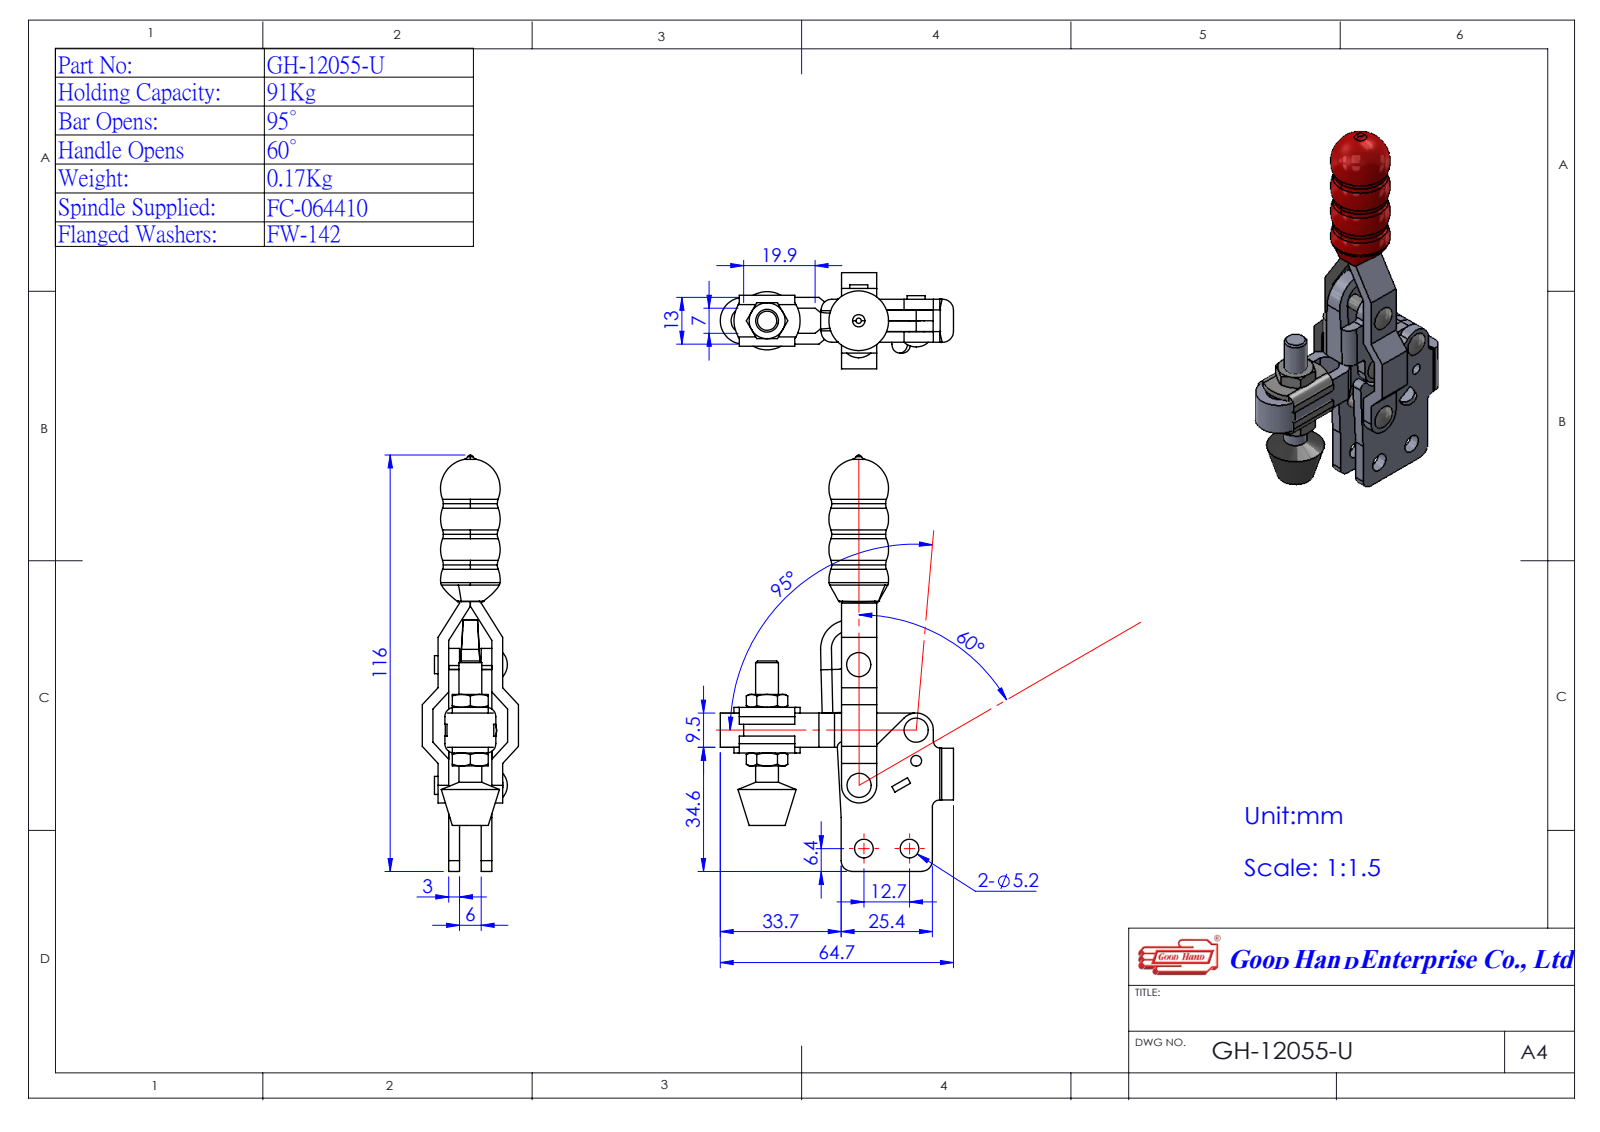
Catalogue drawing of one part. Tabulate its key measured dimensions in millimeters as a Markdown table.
| quantity | value |
| --- | --- |
| part name | Group1^GH-12055-U(簡化)-1; Group5^GH-12055-U(簡化)-1; Group3^GH-12055-U(簡化)-1; Group4^GH-12055-U(簡化)-1 (+2 more) |
| STEP written by | SolidWorks 2016 (AUTOMOTIVE_DESIGN) |
| units | millimeters |
| bodies | 6 solids, 331 faces (138 planar, 117 cylindrical, 76 other) |
| overall size | 115.85 × 64.65 × 26.8 |
| volume | 26 939 mm³ |
| surface area | 18 821 mm² |
| round holes (diameter × count) | 3 × 5, 5.2 × 2 |
| round bosses / shafts (diameter × count) | 5 × 4, 4.05 × 2, 6.35 × 1 |
| partial cylindrical surfaces (radius × count) | 1 × 6, 2.6 × 4, 3.1 × 4, 0.1 × 2, 2 × 2, 3 × 2, 4.5 × 2, 5 × 2 |
| main face-to-face distances | 3, 9, 6, 12, 9.5, 3.5, 6.5, 0.5, 12.5, 2.5 |
| hole center spacings | 24.47, 8.5, 12.7, 15.24, 15.38, 17.41, 17.57, 17.74 |
